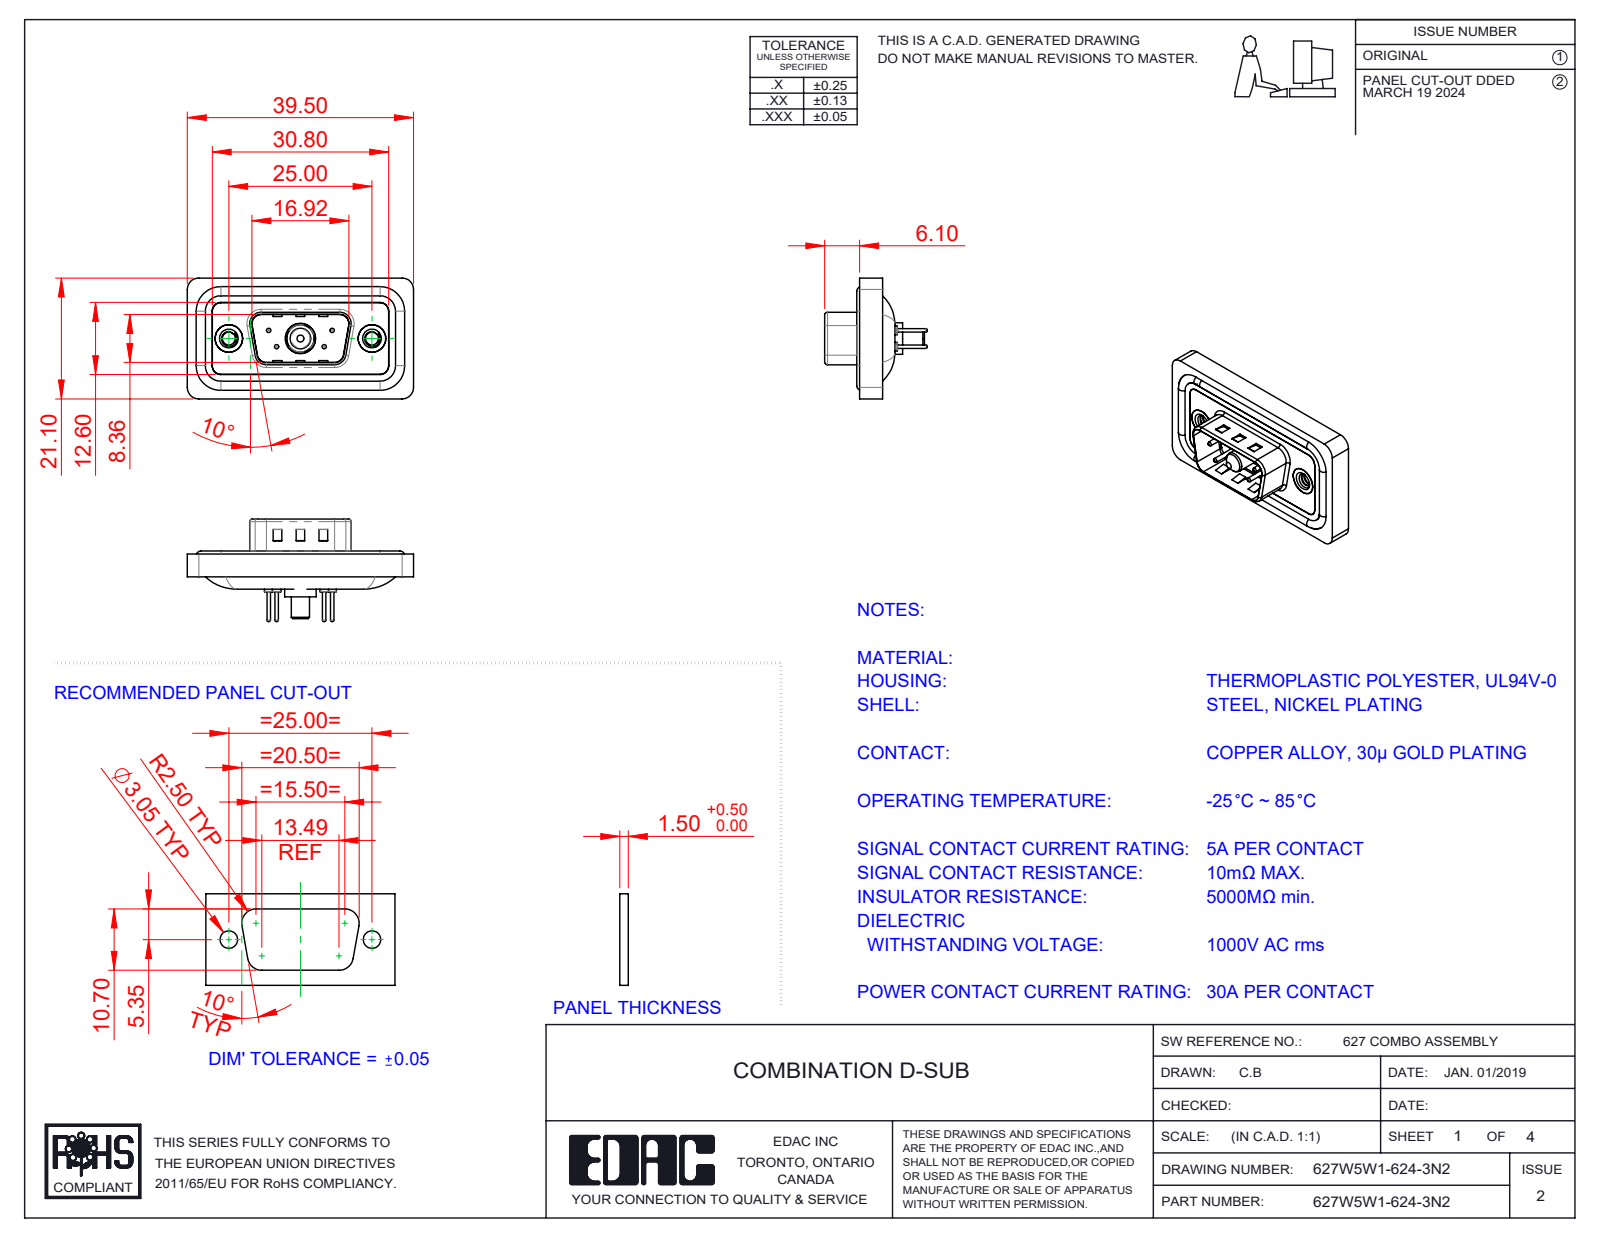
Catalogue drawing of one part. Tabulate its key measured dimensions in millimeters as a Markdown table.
| quantity | value |
| --- | --- |
| part name | 627Combo Shell Rear_09 Contacts; Power Pin_30A S; 627Combo Waterproof Housing_09 Contacts; 627Combo Shell Front_09 Contacts (+5 more) |
| STEP written by | SolidWorks 2023 (CONFIG_CONTROL_DESIGN) |
| units | millimeters |
| bodies | 13 solids, 598 faces (183 planar, 255 cylindrical, 160 other) |
| overall size | 39.5 × 21.1 × 17.9 |
| volume | 4 395 mm³ |
| surface area | 6 946 mm² |
| round holes (diameter × count) | 0.75 × 4, 1.6 × 4, 2 × 4, 2.26 × 2, 4 × 2, 4.8 × 2, 5 × 2, 4.85 × 1, 5.3 × 1 |
| round bosses / shafts (diameter × count) | 1.6 × 4, 1.5 × 4, 0.6 × 4, 4.9 × 2, 5.5 × 1, 5.2 × 1, 4.75 × 1, 3.75 × 1 |
| partial cylindrical surfaces (radius × count) | 1.5 × 22, 2 × 18, 0.5 × 8, 1.6 × 8, 0.25 × 4, 0.6 × 4, 0.65 × 4, 0.9 × 4 |
| main face-to-face distances | 0.4, 1.1, 2.9, 1.6, 3.1, 1.5, 0.5, 2.5, 4, 0.8 |
| hole center spacings | 3.16, 5.72, 7.1, 12.5, 18.1, 4.39, 4.4, 8.31 |
